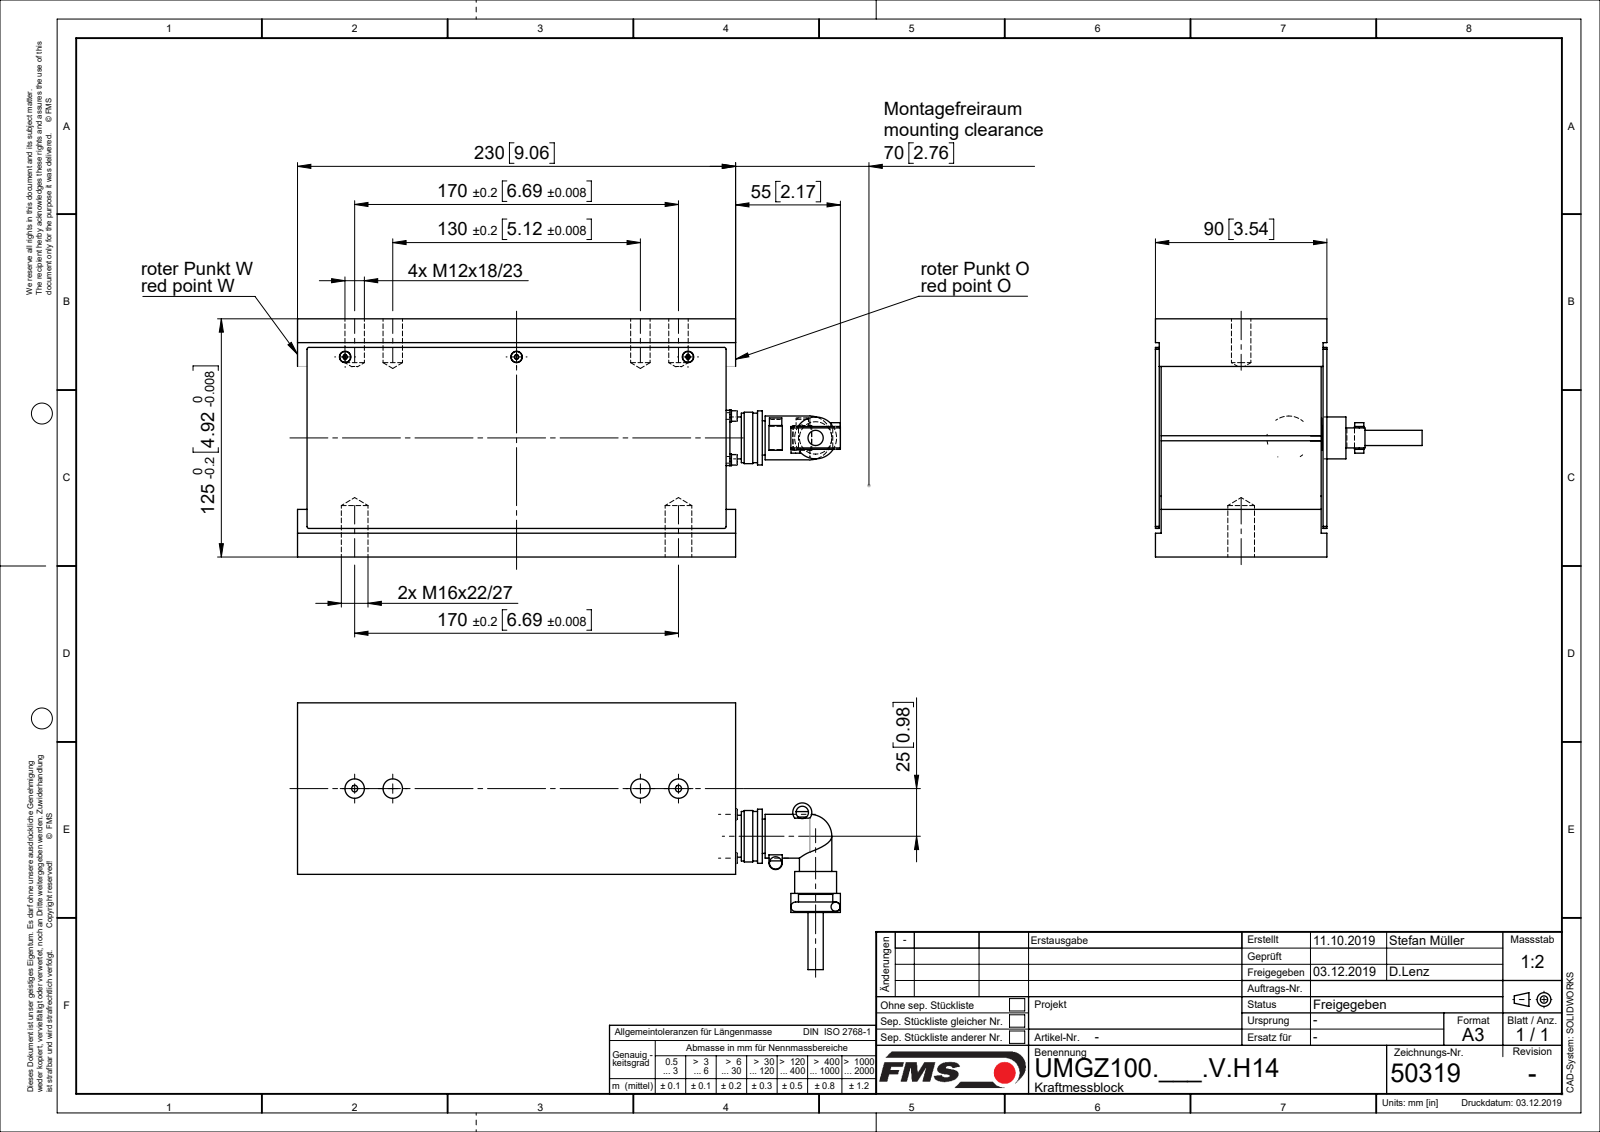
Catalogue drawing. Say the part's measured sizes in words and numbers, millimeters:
The part is named "U50319; U4787104; TEIL1; U47671 (+5 more)". Its 3-D file was written by "Mechanical Desktop 2007 (CONFIG_CONTROL_DESIGN)". It is 18 solids with 400 faces: 155 planar, 158 cylindrical and 87 other. Overall it measures 285 by 125 by 90 millimeters. Its volume is 2 485 000 cubic millimeters and its surface area 229 778 square millimeters. Round holes: 7 of diameter 2.6, 4 of diameter 3.2, 4 of diameter 3.5, 4 of diameter 10.68, 3 of diameter 3.4, 3 of diameter 6, 2 of diameter 14.68, 1 of diameter 23. Round bosses or shafts: 7 of diameter 3, 4 of diameter 6.2, 4 of diameter 5.5, 2 of diameter 22, 2 of diameter 6.5, 2 of diameter 4.8, 1 of diameter 28.4, 1 of diameter 27. Partial cylindrical surfaces (rounded edges, fillets, slot ends): 2 of radius 2.5, 1 of radius 3.5, 1 of radius 5. The main face-to-face distances are 2, 88, 85, 3, 87, 1, 90, 86, 125, 84. The hole center spacings are 16.26, 23, 20, 32.53, 90, 150, 130, 170.
